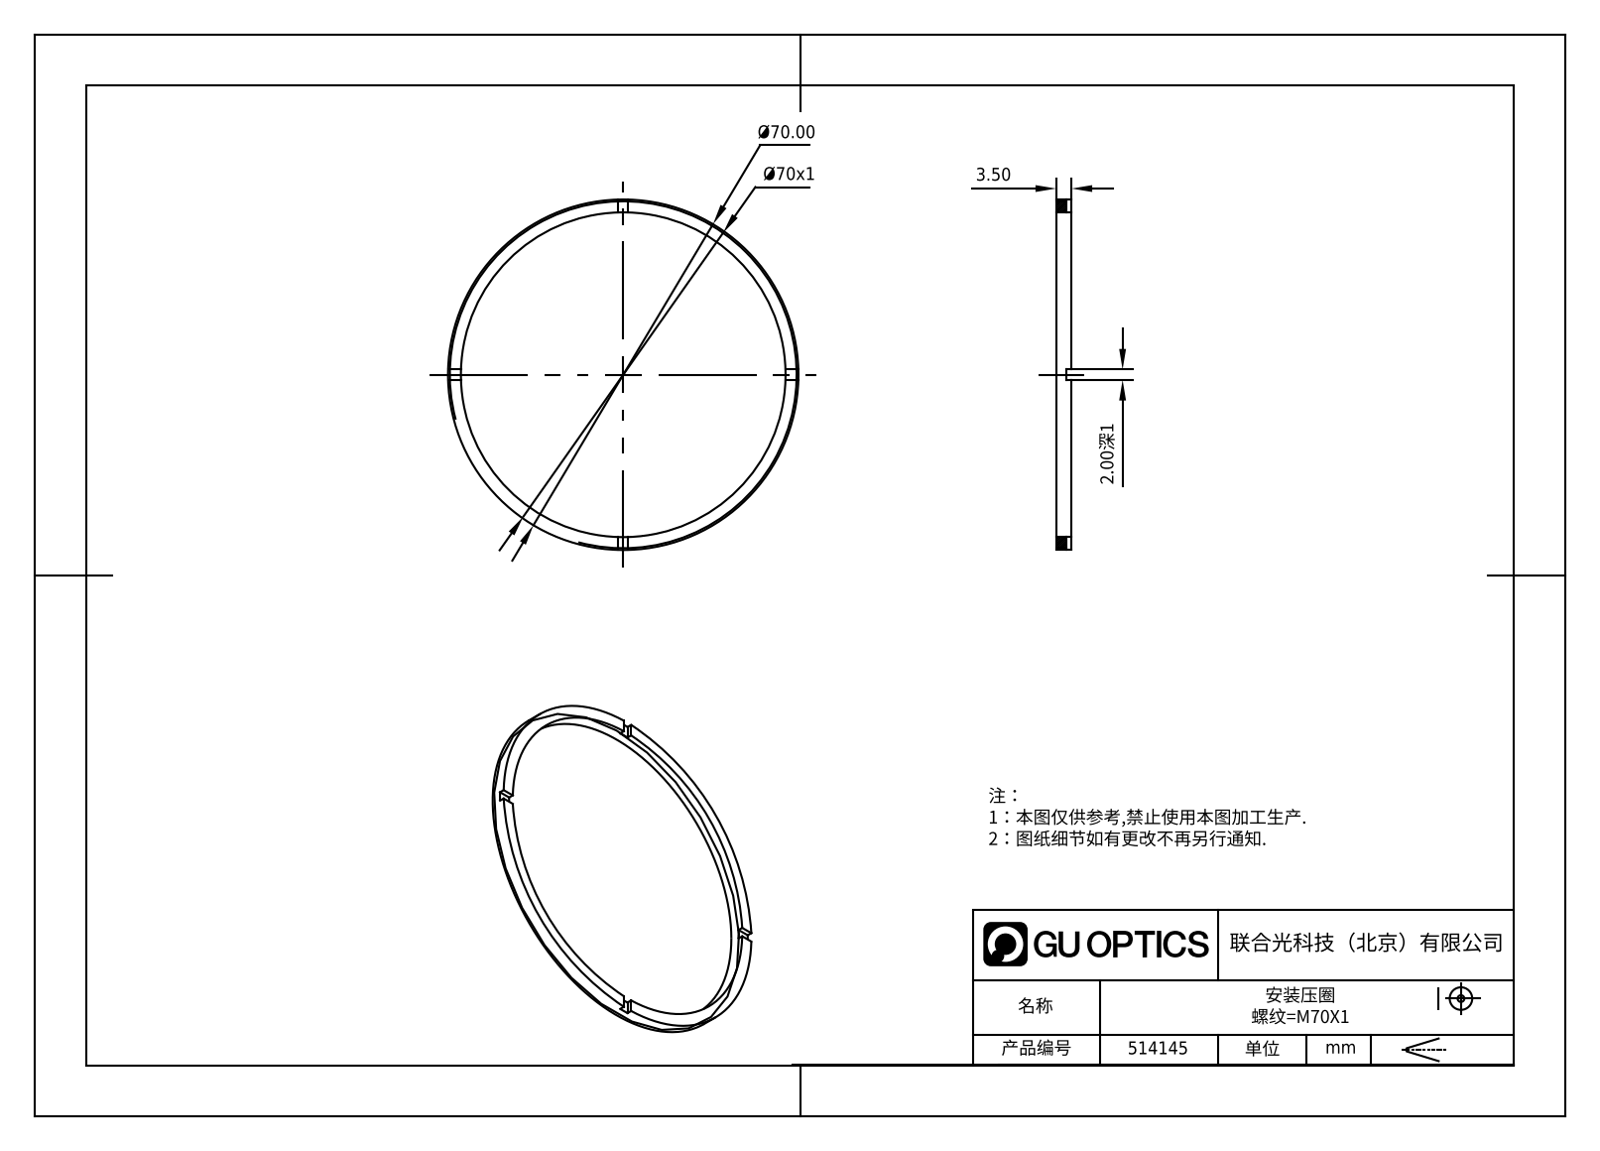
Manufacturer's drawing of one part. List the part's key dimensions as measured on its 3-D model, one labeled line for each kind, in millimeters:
Part name (STEP PRODUCT): 514145
STEP written by: SolidWorks 2020 (CONFIG_CONTROL_DESIGN)
Units: millimetres
Bodies: 1 solid, 21 faces (17 planar, 4 cylindrical, 0 other)
Overall size (bounding box): 70 × 70 × 3.5
Volume: 2 186 mm³ · Surface area: 2 744 mm²
Round holes (diameter × count): ⌀64 ×1
Round bosses / shafts (diameter × count): ⌀70 ×1
Main face-to-face distances: 3.5, 2.5, 1, 2
